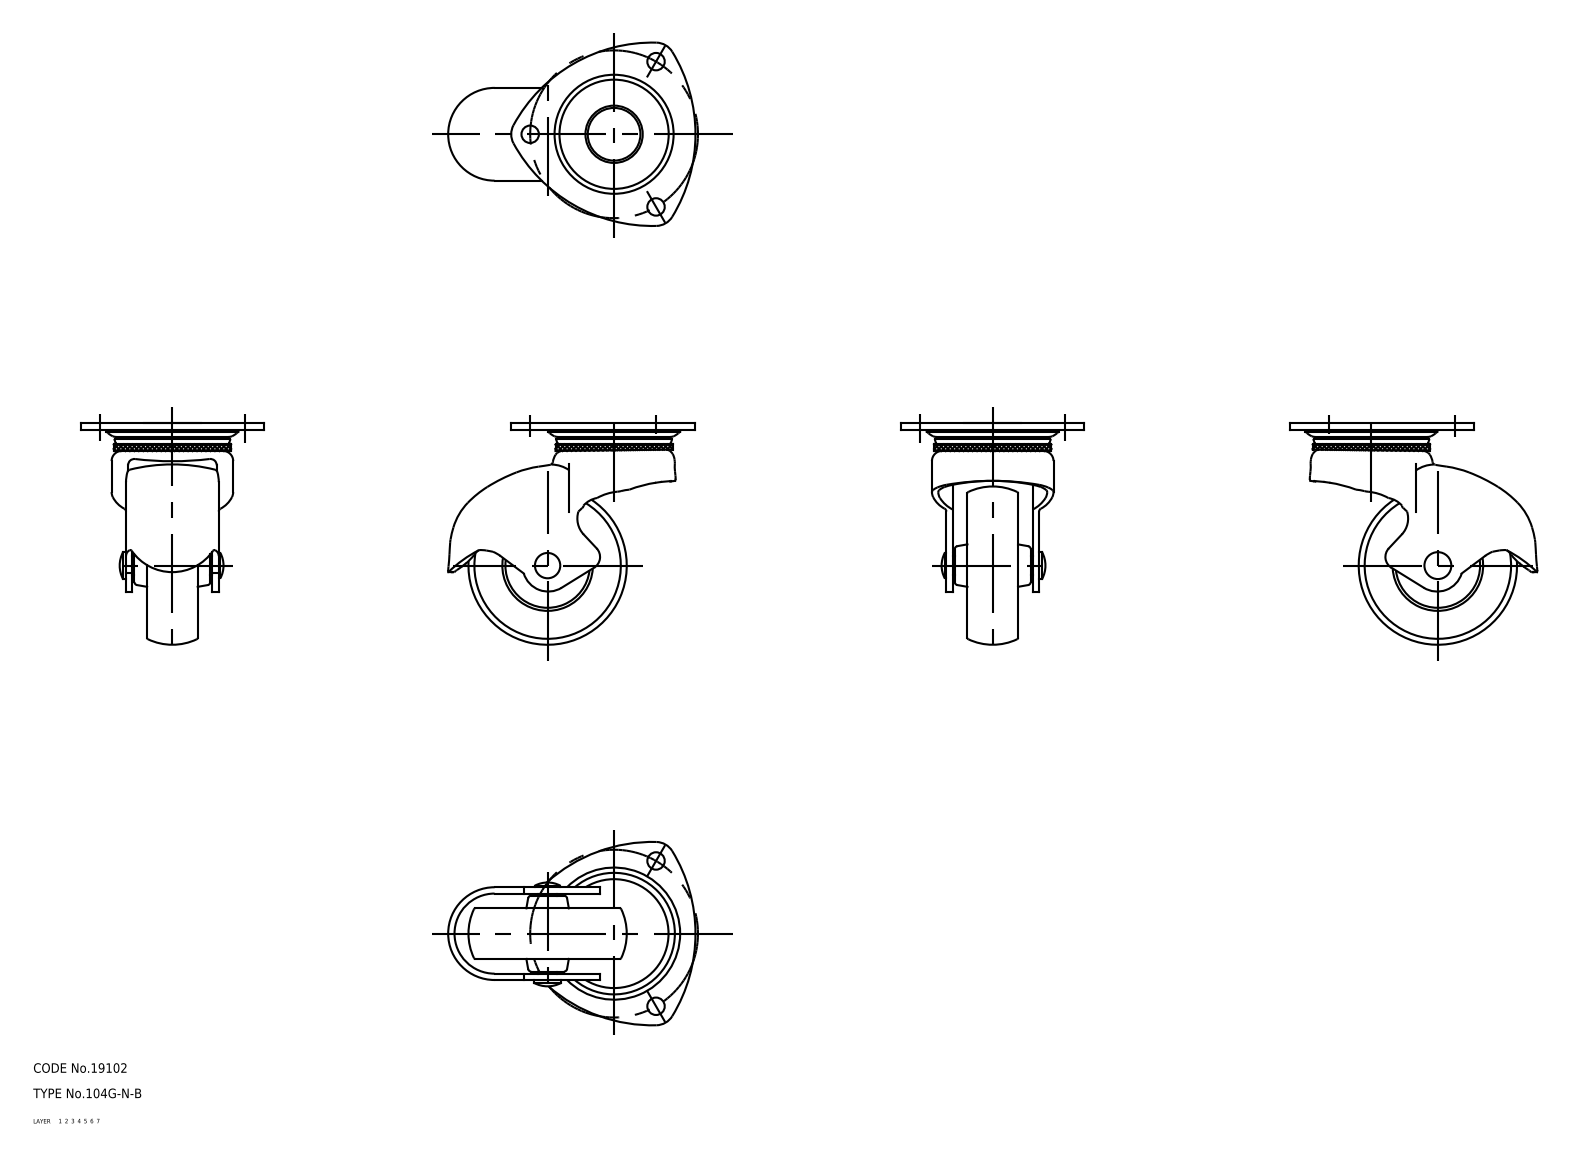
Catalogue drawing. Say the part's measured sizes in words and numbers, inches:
The part is named "wheel; mounting plate; main shaft; axle (+1 more)". Its 3-D file was written by "CADfix (AUTOMOTIVE_DESIGN)". It is 5 solids with 251 faces: 0 planar, 0 cylindrical and 251 other. Overall it measures 3.075 by 2.756 by 2.281 inches. Its volume is 3.258 cubic inches and its surface area 42.64 square inches.
